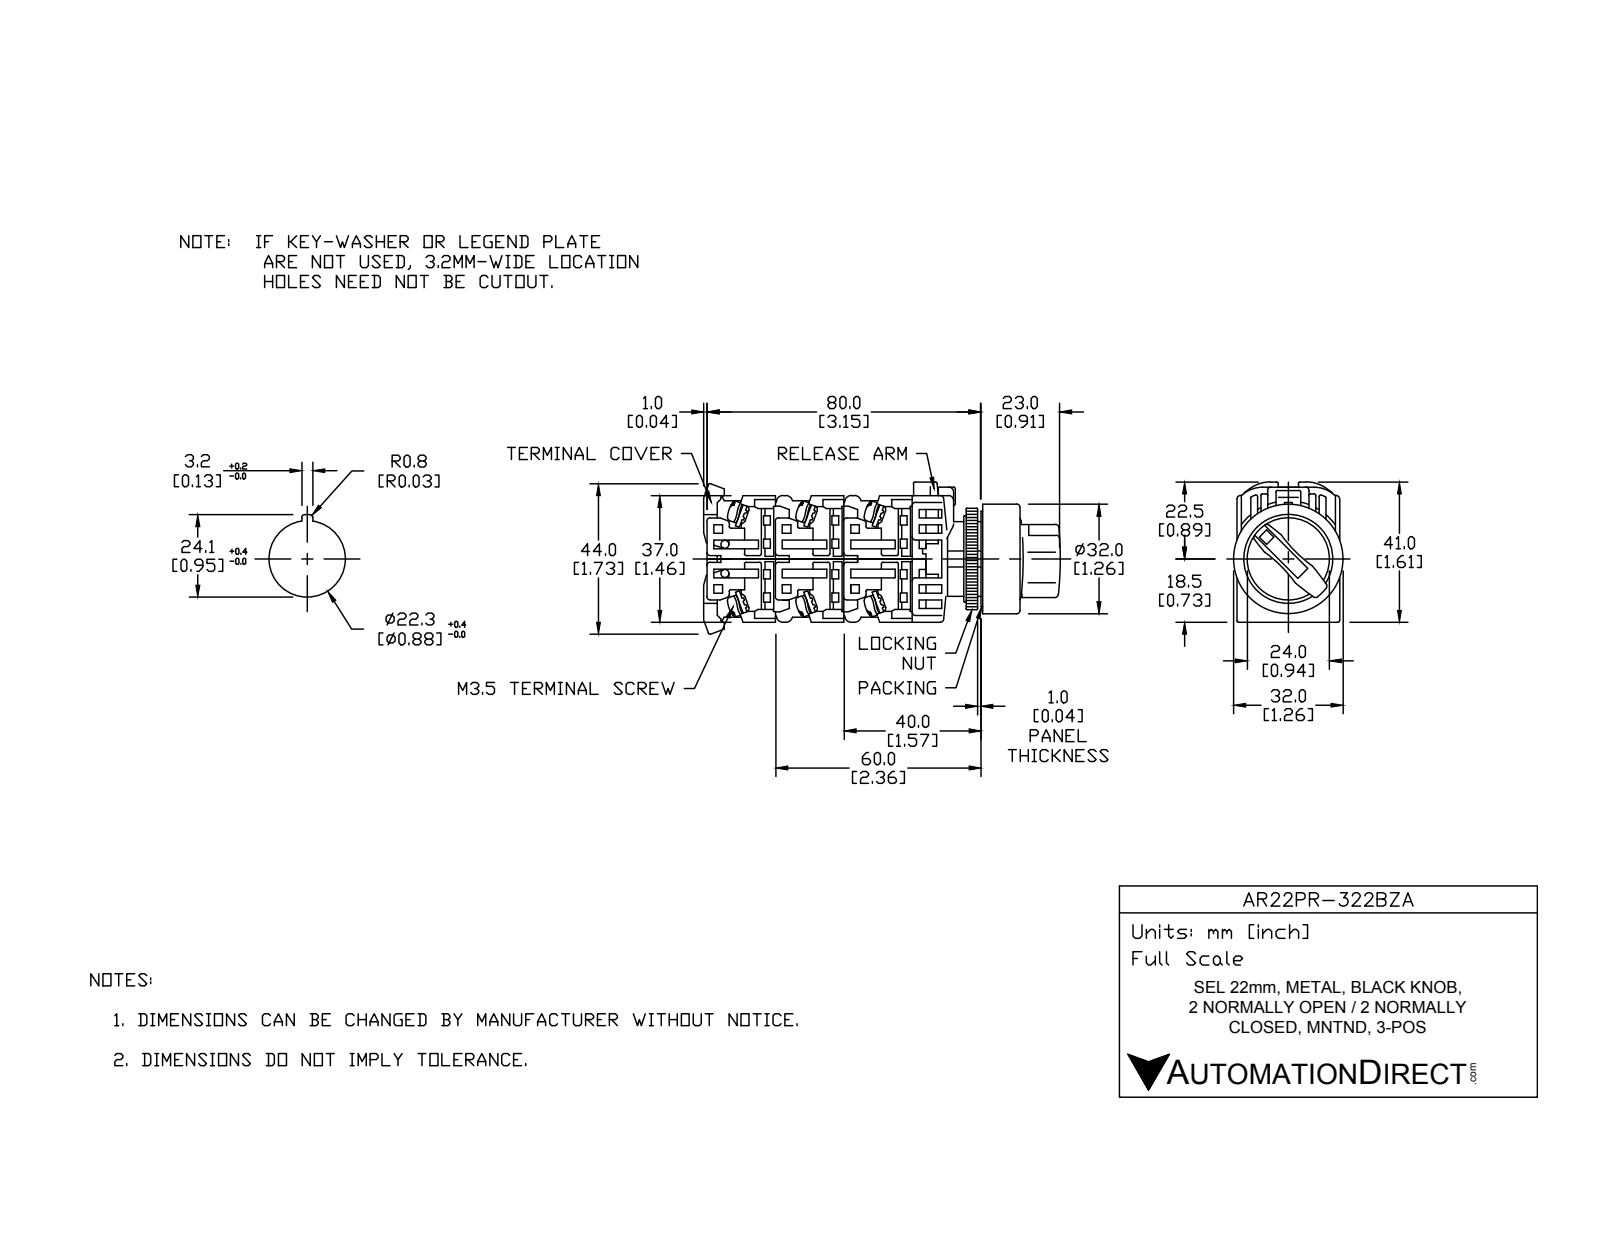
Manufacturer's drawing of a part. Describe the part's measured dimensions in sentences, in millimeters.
The part is named "AR22PR-322BZA". Its 3-D file was written by "SolidWorks 2017 (AUTOMOTIVE_DESIGN)". It is 18 solids with 463 faces: 317 planar, 118 cylindrical and 28 other. Overall it measures 64 by 43.81 by 32 millimeters. Its volume is 38 439 cubic millimeters and its surface area 24 800 square millimeters. Round holes: 1 of diameter 21.8, 1 of diameter 22, 1 of diameter 25, 1 of diameter 31. Round bosses or shafts: 4 of diameter 5, 1 of diameter 32, 1 of diameter 30.5, 1 of diameter 29.8, 1 of diameter 24, 1 of diameter 21.75, 1 of diameter 17. Partial cylindrical surfaces (rounded edges, fillets, slot ends): 39 of radius 0.5, 8 of radius 1.75, 6 of radius 1, 4 of radius 5, 2 of radius 4, 1 of radius 12, 1 of radius 16.59, 1 of radius 17.59. The main face-to-face distances are 1, 18, 3, 28.5, 48.5, 20, 29, 0.5, 21, 10.
